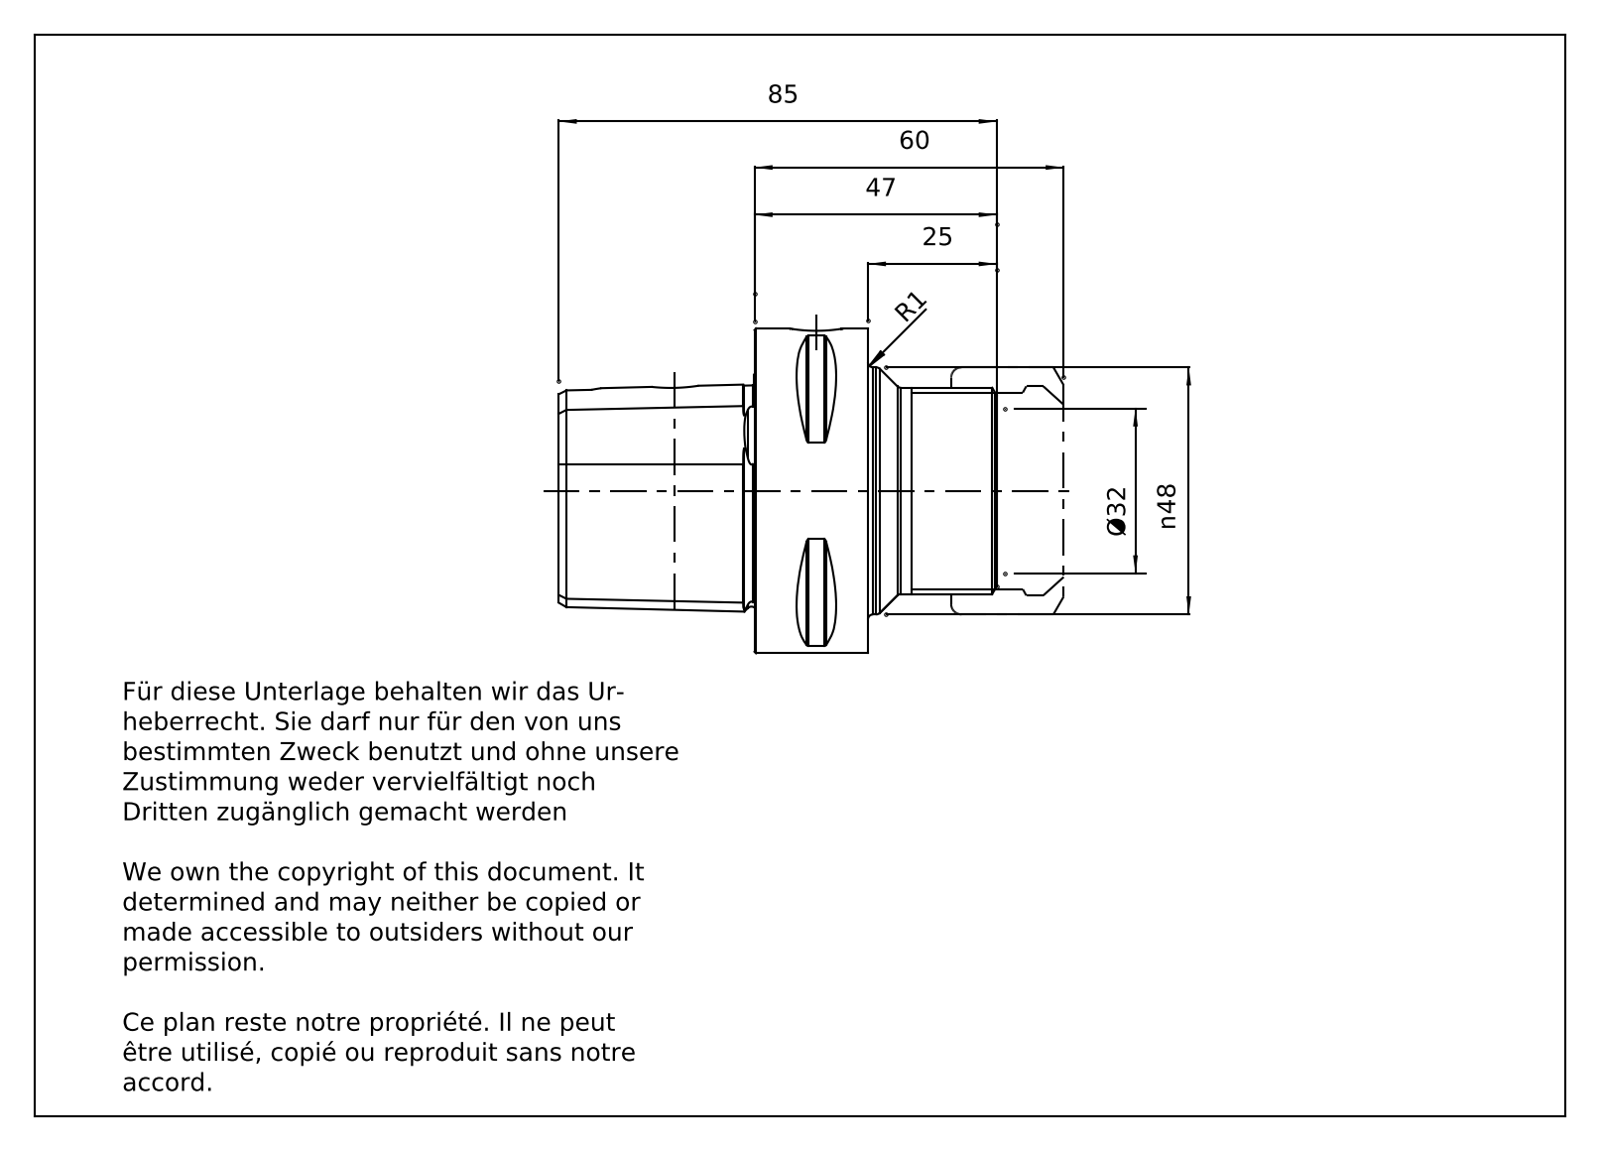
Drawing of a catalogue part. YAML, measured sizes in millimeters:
part_name: "CC6-025-32; 83-912-32; CC6-025-32_ASM"
step_written_by: "PRO/ENGINEER BY PARAMETRIC TECHNOLOGY CORPORATION, 2010430 (CONFIG_CONTROL_DESIGN)"
units: millimeters
bodies: {solids: 2, faces: 168, planar: 49, cylindrical: 43, other: 76}
overall_size: [98, 63, 63]
volume: 150861
surface_area: 33340
round_holes:
  - {diameter: 4.25, count: 1}
  - {diameter: 8.1, count: 1}
  - {diameter: 10.04, count: 1}
  - {diameter: 18, count: 1}
  - {diameter: 23.5, count: 1}
  - {diameter: 28.02, count: 1}
  - {diameter: 32, count: 1}
round_bosses_or_shafts:
  - {diameter: 63, count: 1}
  - {diameter: 50, count: 1}
  - {diameter: 48, count: 1}
  - {diameter: 40, count: 1}
  - {diameter: 20, count: 1}
partial_cylinders:
  - {radius: 0.5, count: 8}
  - {radius: 2.7, count: 6}
  - {radius: 6, count: 1}
face_to_face_distances: [38, 60, 37.5, 22, 15.5, 22.5, 47, 13, 25, 9.5]
hole_center_spacings: [27.5]
